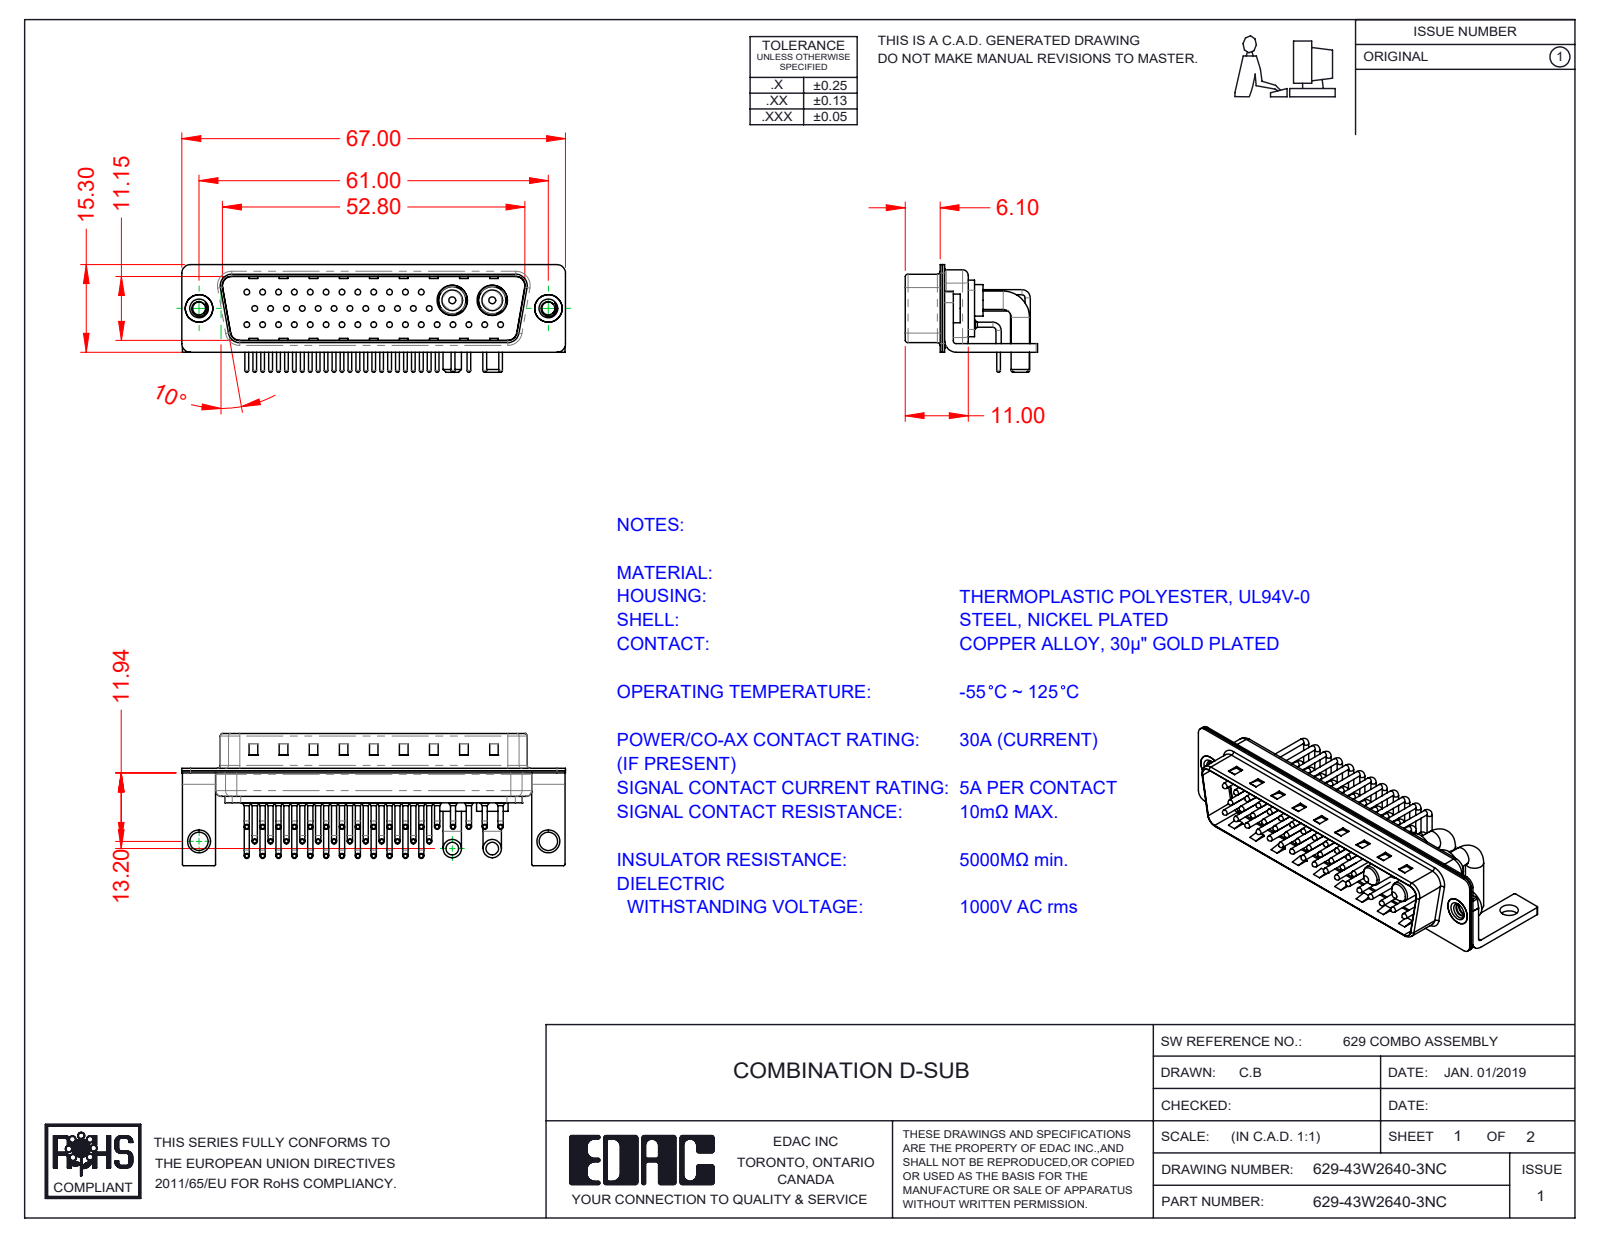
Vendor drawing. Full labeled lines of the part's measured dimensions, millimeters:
Part name (STEP PRODUCT): 629Combo Housing_43W2; Power Pin_30A RA 50; 629Combo Shell Front_50 Contacts; 629Combo Contact Row 3 (+6 more)
STEP written by: SolidWorks 2020 (CONFIG_CONTROL_DESIGN)
Units: millimetres
Bodies: 52 solids, 5056 faces (2867 planar, 1683 cylindrical, 506 other)
Overall size (bounding box): 67 × 23.1 × 18.8
Volume: 5 658 mm³ · Surface area: 13 388 mm²
Round holes (diameter × count): ⌀0.75 ×41, ⌀1.6 ×41, ⌀2 ×41, ⌀2.26 ×2, ⌀3.2 ×2, ⌀4 ×2, ⌀4.8 ×2, ⌀4.85 ×2, ⌀5.3 ×2
Round bosses / shafts (diameter × count): ⌀0.9 ×82, ⌀1.5 ×41, ⌀1 ×41, ⌀0.65 ×41, ⌀3.2 ×4, ⌀5.5 ×2, ⌀5.2 ×2, ⌀5 ×2
Partial cylindrical surfaces — rounded edges, fillets, slot ends (radius × count): R1.01 ×41, R0.25 ×16, R1.5 ×16, R2 ×13, R0.5 ×9, R1.6 ×8, R0.6 ×4, R0.65 ×4
Main face-to-face distances: 0.4, 1.5, 11.55, 5.6, 5.2, 0.8, 4.1, 6, 0.78, 1.9
Hole centre spacings: 2.77, 5.54, 3.16, 8.31, 11.08, 13.85, 16.62, 19.39
